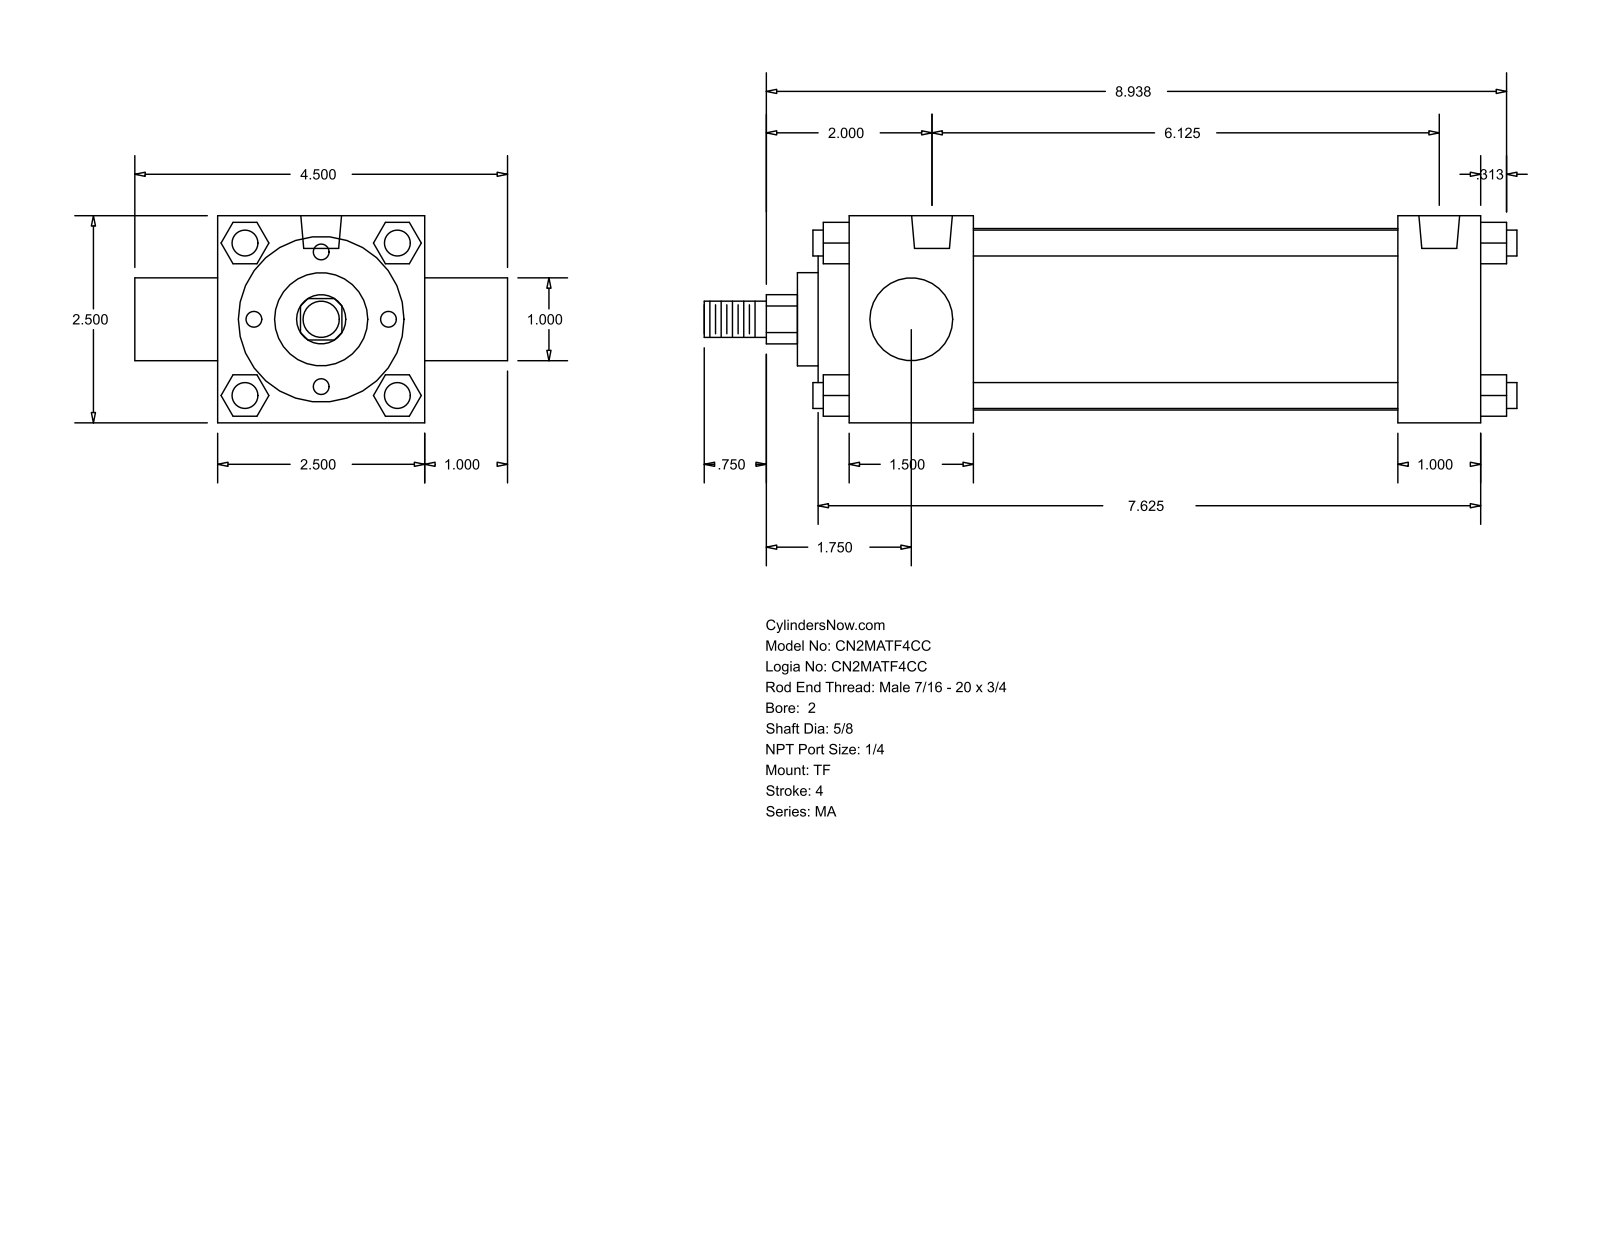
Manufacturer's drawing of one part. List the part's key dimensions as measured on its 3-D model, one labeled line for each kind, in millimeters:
Part name (STEP PRODUCT): MA_TF__0200_0.625
STEP written by: GSSL Pune (CONFIG_CONTROL_DESIGN)
Units: millimetres
Bodies: 0 solids, 122 faces (93 planar, 29 cylindrical, 0 other)
Overall size (bounding box): 249.24 × 114.3 × 63.5
Round holes (diameter × count): ⌀7.94 ×3, ⌀12.49 ×2
Round bosses / shafts (diameter × count): ⌀7.94 ×4, ⌀55.63 ×1, ⌀50.8 ×1, ⌀28.57 ×1, ⌀25.4 ×1, ⌀15.88 ×1, ⌀11.11 ×1
Partial cylindrical surfaces — rounded edges, fillets, slot ends (radius × count): R7.54 ×1
Main face-to-face distances: 63.5, 38.1, 12.7, 193.67, 168.28, 130.18, 155.57, 25.39, 9.52, 47.62
Hole centre spacings: 155.58
